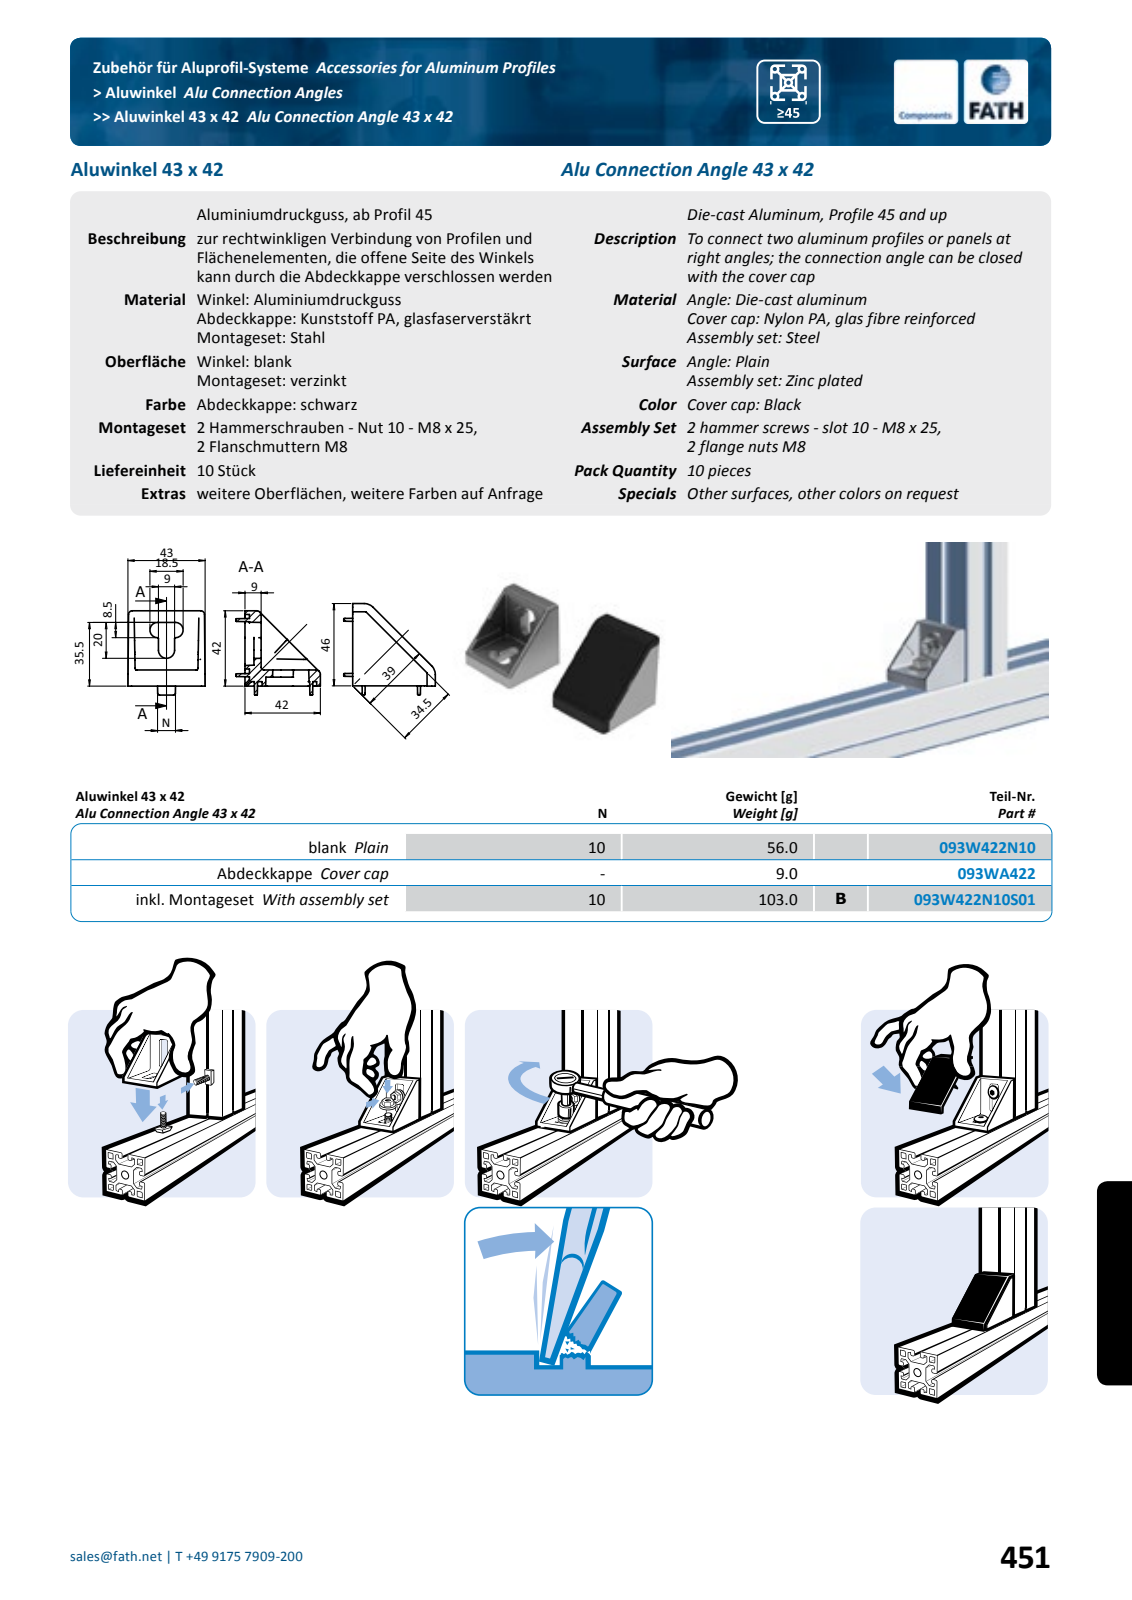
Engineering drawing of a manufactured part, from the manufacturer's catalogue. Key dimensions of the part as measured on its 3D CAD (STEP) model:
Part name (STEP PRODUCT): fath_093w422n10
STEP written by: Spatial InterOp 3D (automotive_design)
Units: millimetres
Bodies: 1 solid, 522 faces (100 planar, 184 cylindrical, 238 other)
Overall size (bounding box): 45.84 × 45.84 × 43
Volume: 21 094 mm³ · Surface area: 12 013 mm²
Partial cylindrical surfaces — rounded edges, fillets, slot ends (radius × count): R1 ×58, R0.3 ×54, R0.5 ×24, R2 ×8, R4.25 ×4, R2.2 ×2, R1.04 ×1, R1.5 ×1
Main face-to-face distances: 9, 4, 5, 42, 37, 33, 30.89, 9.06, 21.83, 35.25
